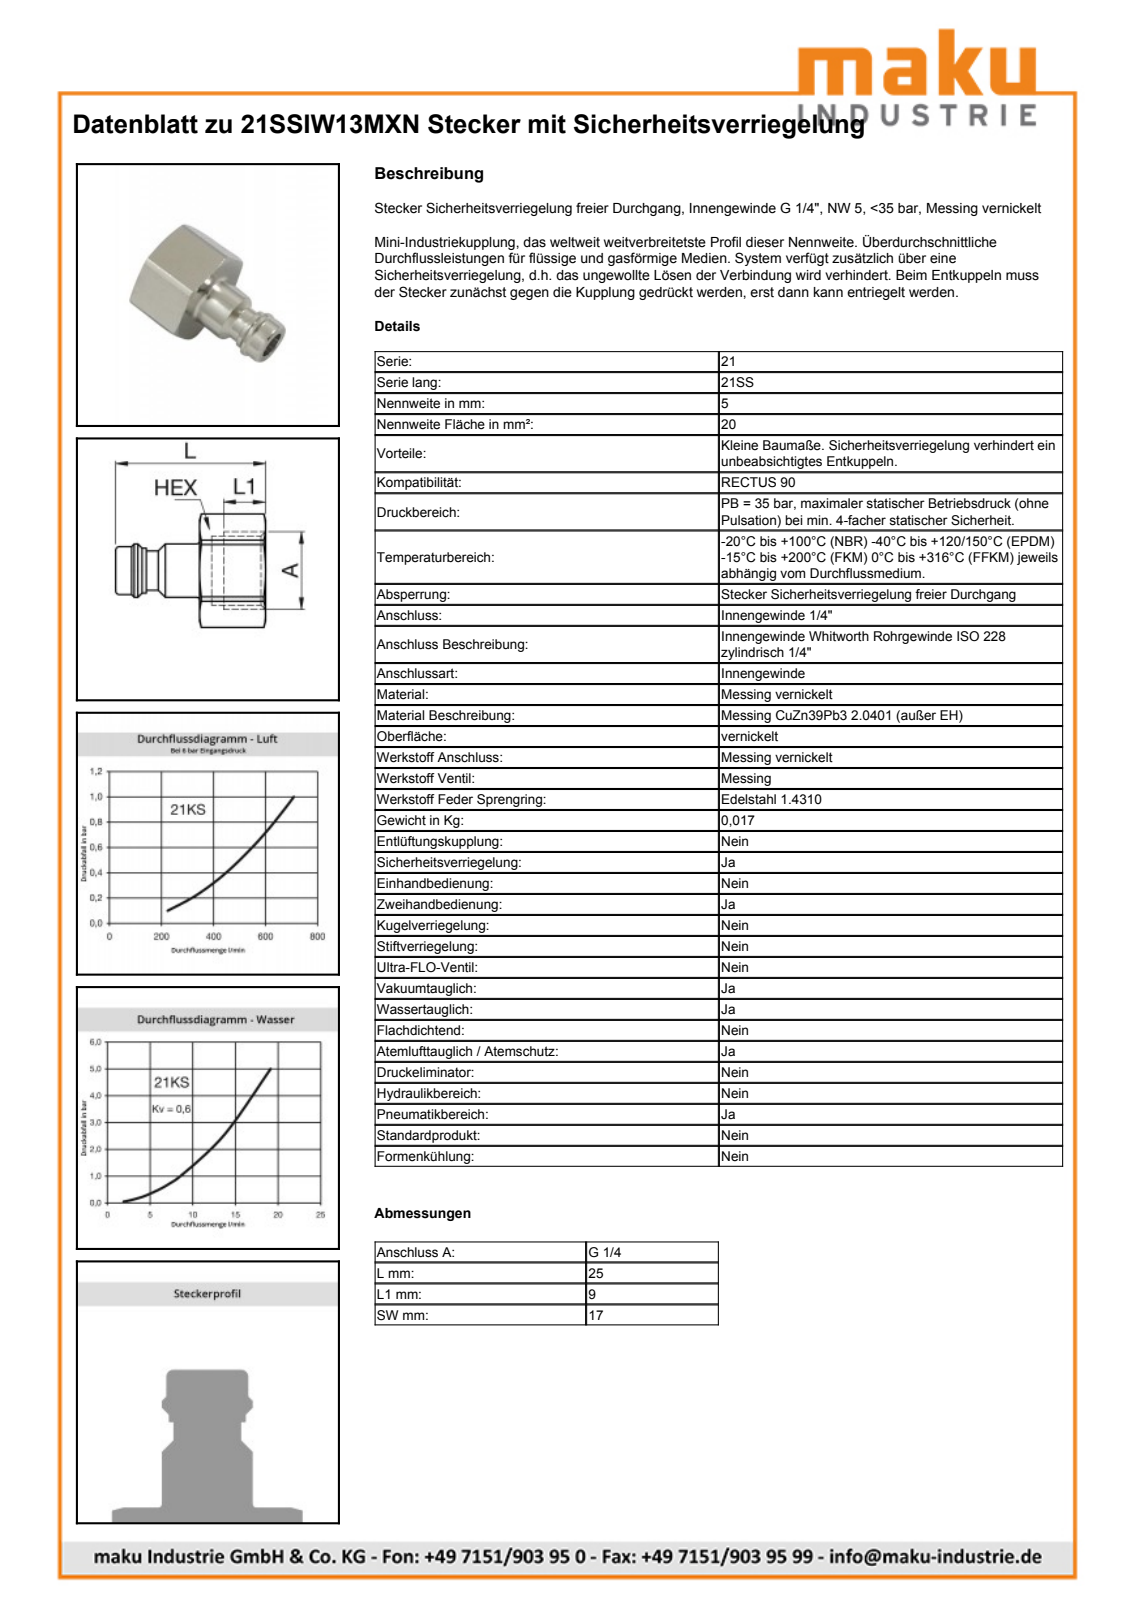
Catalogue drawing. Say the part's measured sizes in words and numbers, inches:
The part is named "D105018". Its 3-D file was written by "Autodesk Inventor 2011 (AUTOMOTIVE_DESIGN)". It is 1 solid with 42 faces: 11 planar, 13 cylindrical and 18 other. Overall it measures 0.984 by 0.754 by 0.669 inches. Its volume is 0.136 cubic inches and its surface area 3.129 square inches. Round holes: 1 of diameter 0.197, 1 of diameter 0.451. Round bosses or shafts: 1 of diameter 0.354, 1 of diameter 0.319, 1 of diameter 0.299, 1 of diameter 0.262. Partial cylindrical surfaces (rounded edges, fillets, slot ends): 1 of radius 0.377. The main face-to-face distances are 0.669, 0.429, 0.354, 0.075, 0.555, 0.63, 0.984, 0.201, 0.783.
